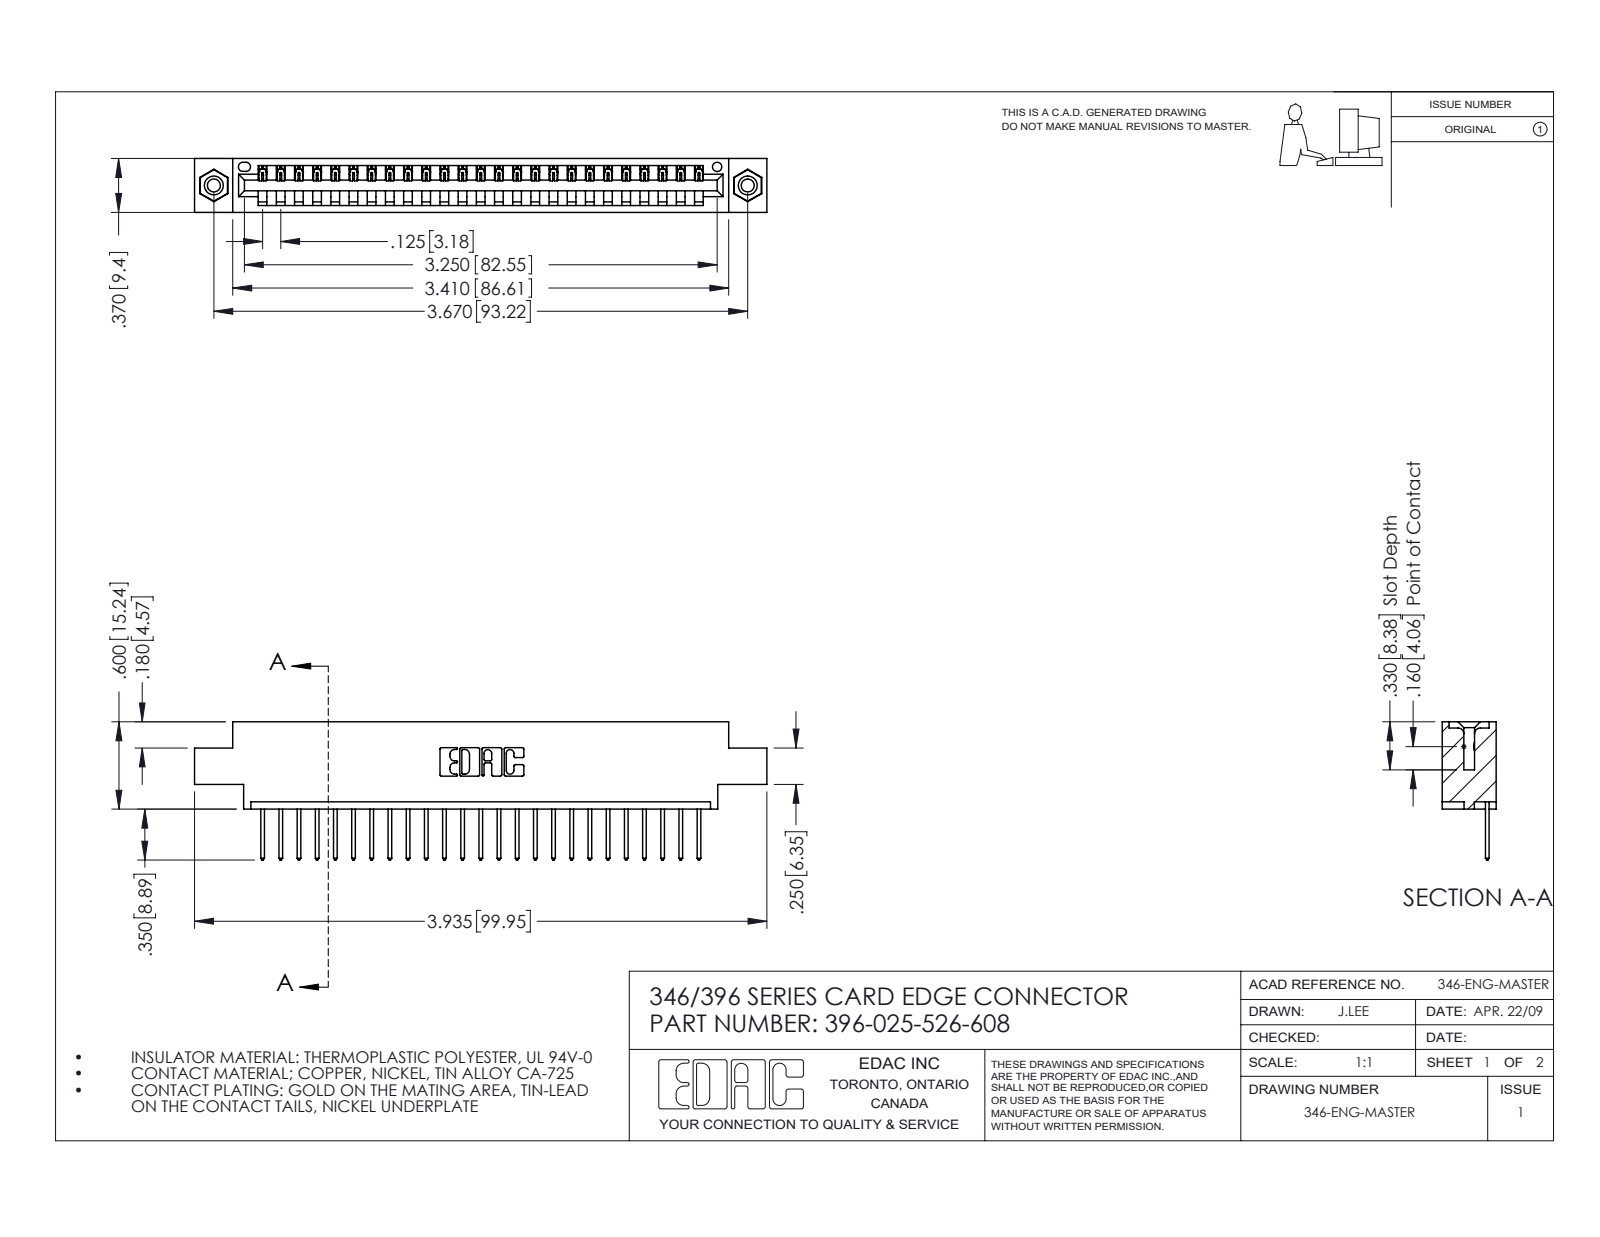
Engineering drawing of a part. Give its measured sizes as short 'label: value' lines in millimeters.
name: 396-025-526-608; 345-292-001_345-293-126; 345-250-001_345-250-003-102; 346 Part_0.170 Offset - 0.156 Dia-TI
written by: SolidWorks 2016 (CONFIG_CONTROL_DESIGN)
unit: mm
bodies: 28 solids, 1636 faces (1112 planar, 508 cylindrical, 16 other)
size: 99.9 × 24.1 × 9.4
volume: 9 280 mm³; area: 11 560 mm²
holes: 2× ⌀2.3, 2× ⌀3.2, 2× ⌀4, 1× ⌀1.6
bosses: 2× ⌀3.9
rounds: 50× R0.2, 50× R0.3, 22× R0.3, 6× R0.2, 6× R0.8, 3× R0.7, 2× R0.8, 2× R1
face distances: 1.2, 8.2, 9.4, 6.4, 1.8, 7.6, 0.6, 5.6, 3.8, 2.5
hole spacings: 6.2, 87.9, 93.2
